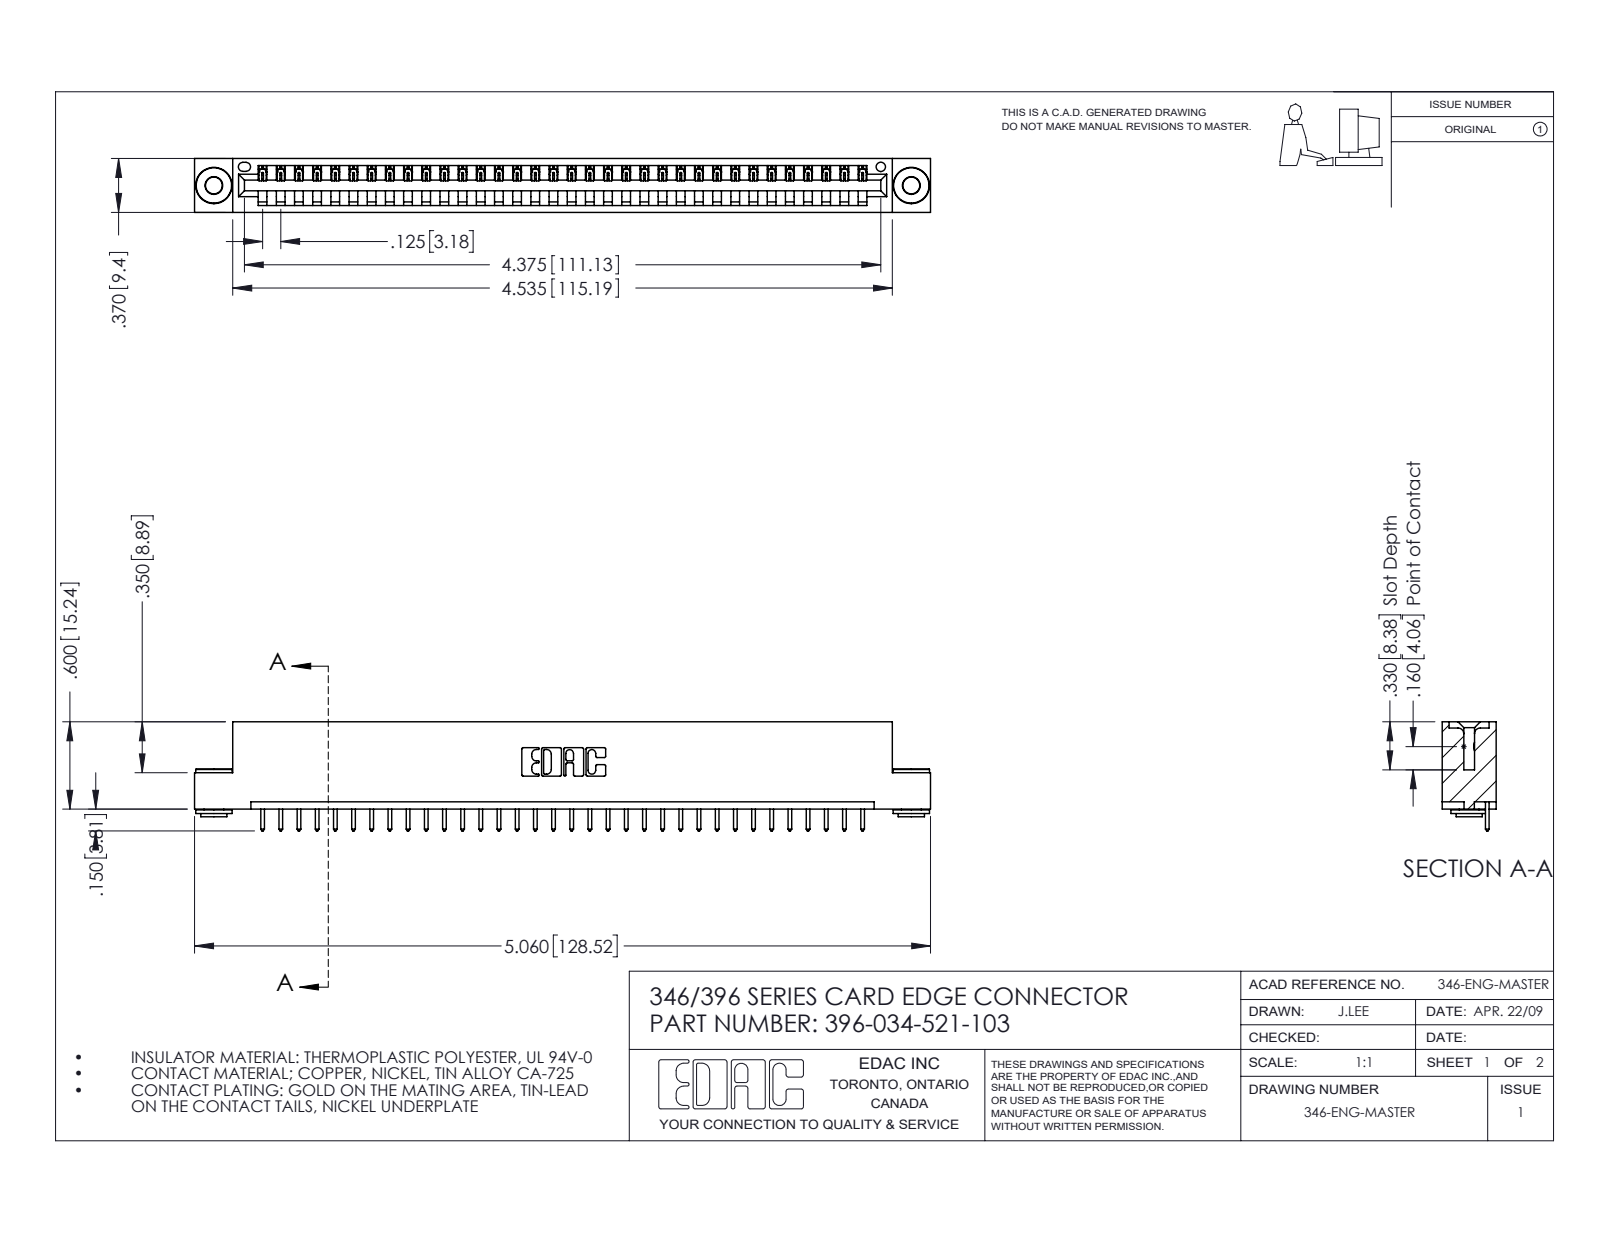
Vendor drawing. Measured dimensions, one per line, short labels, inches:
name: 345-292-001_345-293-121; 346 Part_Flush Mounting Lugs - 0.156 Dia-TH; 396-034-521-103; 345-250-002_345-250-002-102
written by: SolidWorks 2016 (CONFIG_CONTROL_DESIGN)
unit: in
bodies: 37 solids, 2132 faces (1446 planar, 678 cylindrical, 8 other)
size: 5.06 × 0.75 × 0.37
volume: 0.743 in³; area: 23.19 in²
holes: 2× ⌀0.116, 2× ⌀0.156, 1× ⌀0.064
bosses: 2× ⌀0.25, 2× ⌀0.18, 2× ⌀0.136
rounds: 68× R0.006, 68× R0.01, 22× R0.01, 6× R0.007, 6× R0.031, 3× R0.026, 2× R0.031, 2× R0.04
face distances: 0.048, 0.322, 0.37, 0.25, 0.025, 0.072, 0.298, 0.148, 0.222, 0.1
hole spacings: 0.246, 4.587, 4.795
